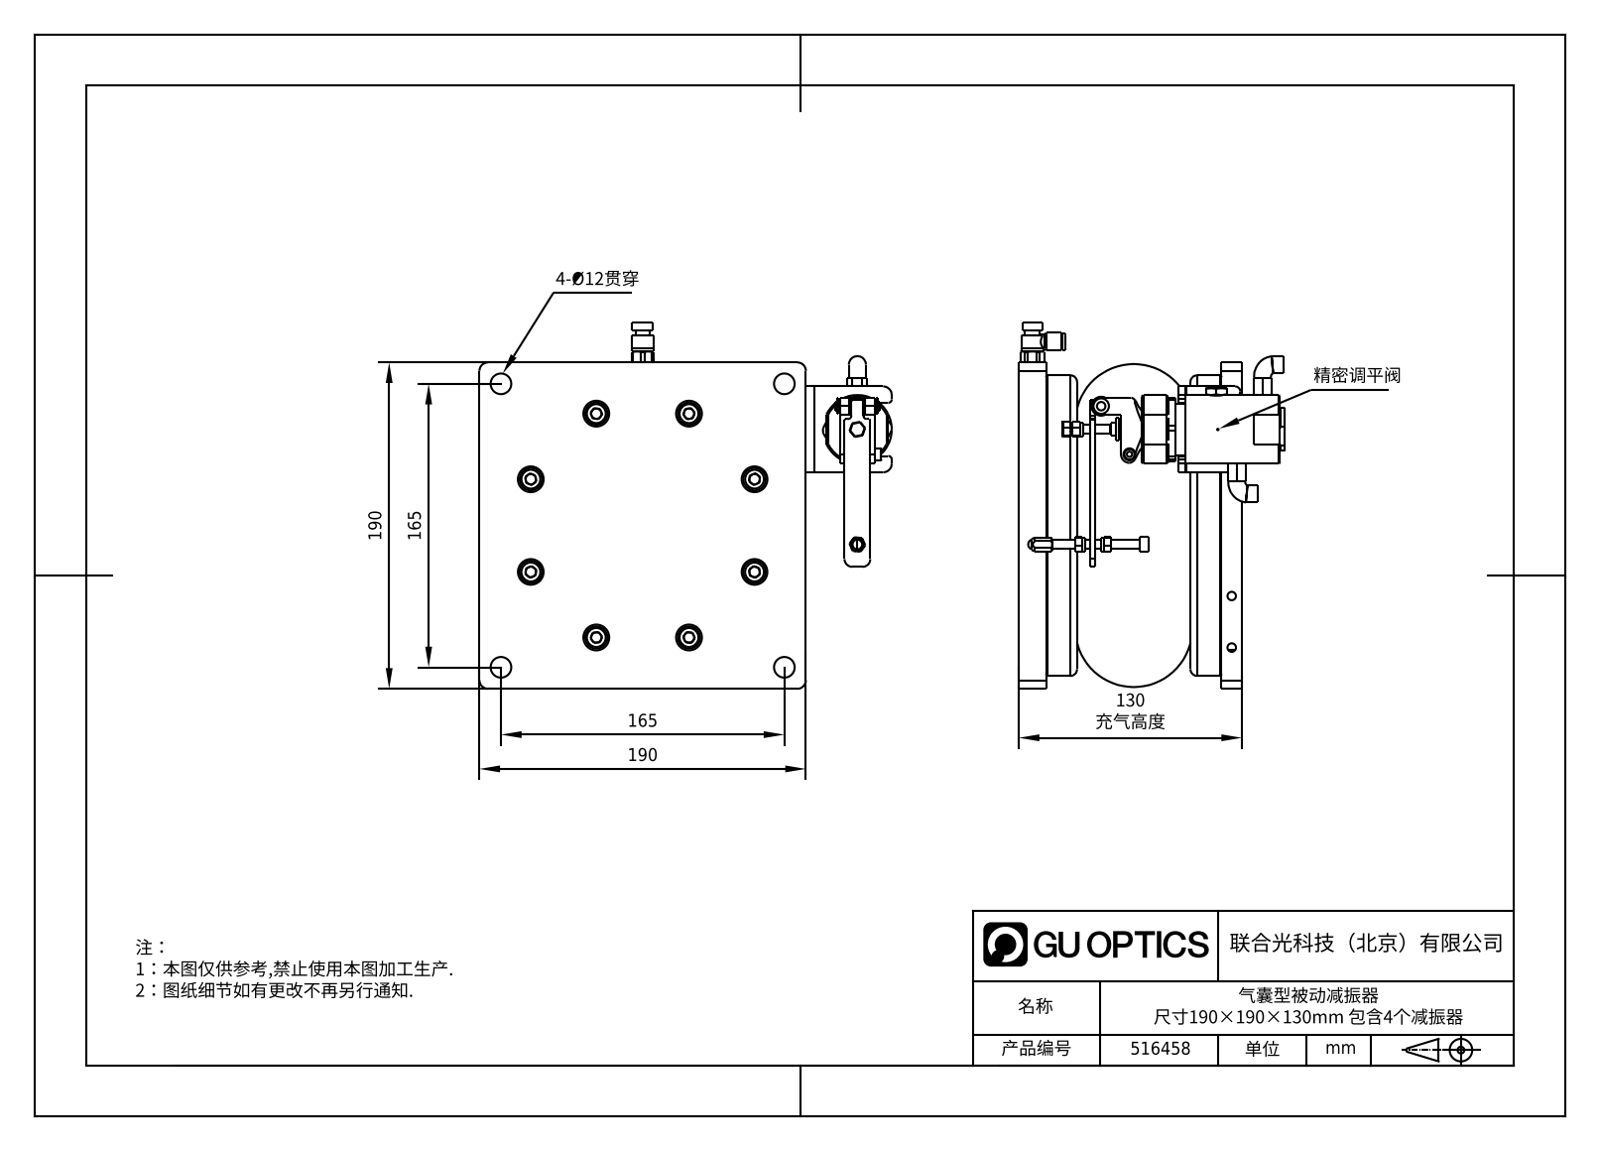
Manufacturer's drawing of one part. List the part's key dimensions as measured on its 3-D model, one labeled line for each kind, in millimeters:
Part name (STEP PRODUCT): 516458
STEP written by: SolidWorks 2020 (CONFIG_CONTROL_DESIGN)
Units: millimetres
Bodies: 0 solids, 531 faces (328 planar, 124 cylindrical, 79 other)
Overall size (bounding box): 240 × 213.5 × 155
Round holes (diameter × count): ⌀15 ×8, ⌀5 ×4, ⌀12 ×4, ⌀11.5 ×2, ⌀8 ×1, ⌀9.7 ×1, ⌀13 ×1, ⌀40 ×1, ⌀175 ×1
Round bosses / shafts (diameter × count): ⌀6.8 ×8, ⌀10 ×4, ⌀8 ×2, ⌀7 ×2, ⌀30 ×1, ⌀13 ×1, ⌀12.7 ×1, ⌀12.6 ×1
Partial cylindrical surfaces — rounded edges, fillets, slot ends (radius × count): R5 ×10, R0.3 ×6, R2 ×3, R3 ×2, R4.5 ×2, R0.74 ×1, R4.74 ×1, R7 ×1
Main face-to-face distances: 12, 102, 118, 16, 130, 114, 18, 84, 30, 34
Hole centre spacings: 58.17, 110.85, 53.96, 70.5, 99.7, 157.72, 183.79, 116.67
